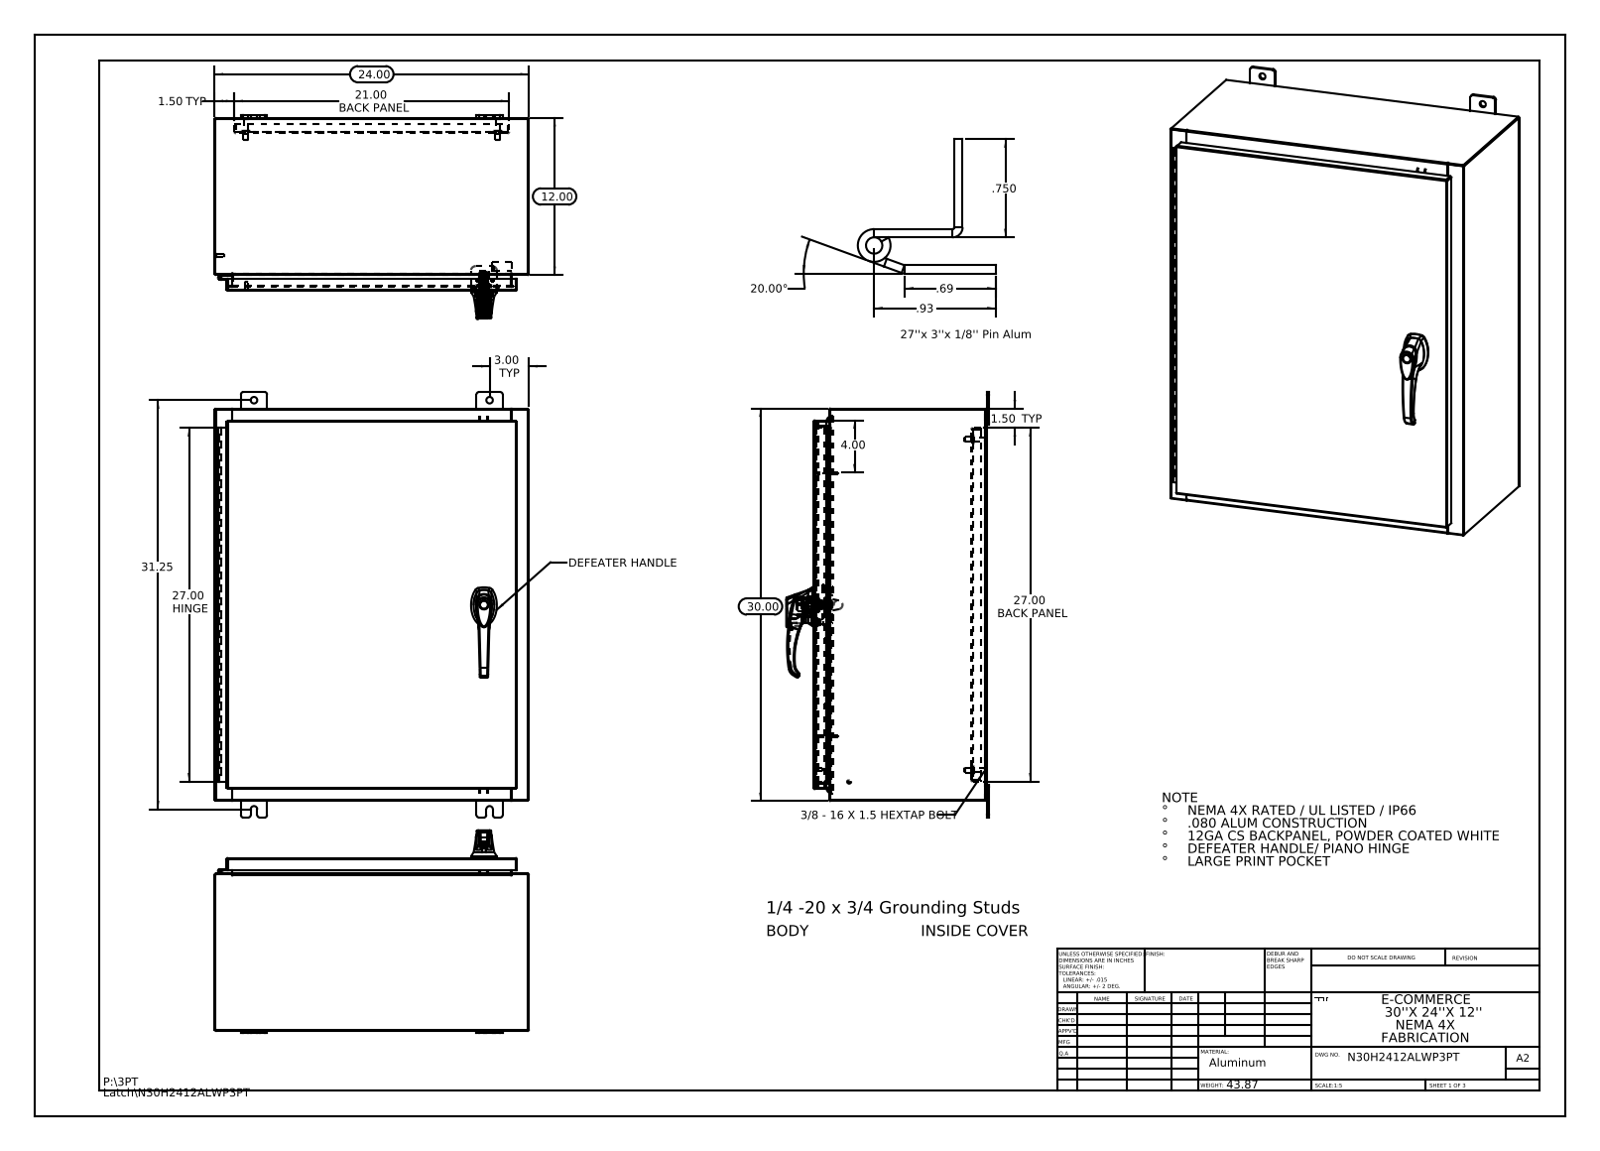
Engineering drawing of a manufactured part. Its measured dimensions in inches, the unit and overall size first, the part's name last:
Units: inches
Overall size (bounding box): 32.5 × 24 × 15.495
Round holes (diameter × count): ⌀0.5 ×8, ⌀0.25 ×4, ⌀0.138 ×3, ⌀0.161 ×3, ⌀0.079 ×2, ⌀0.203 ×2, ⌀0.313 ×2, ⌀0.437 ×2, ⌀0.125 ×1, ⌀0.125 ×1, ⌀0.197 ×1, ⌀0.276 ×1
Round bosses / shafts (diameter × count): ⌀0.625 ×4, ⌀0.375 ×4, ⌀0.33 ×4, ⌀0.157 ×4, ⌀0.14 ×4, ⌀0.315 ×3, ⌀0.236 ×3, ⌀1.181 ×1
Partial cylindrical surfaces — rounded edges, fillets, slot ends (radius × count): R0.118 ×37, R0.006 ×33, R0.013 ×24, R0.19 ×24, R0.088 ×18, R0.039 ×15, R0.028 ×12, R0.008 ×6
Main face-to-face distances: 0.075, 13.126, 23.925, 0.104, 13.051, 13.201, 1, 29.925, 1.075, 12.051
Hole centre spacings: 8.369, 0.295, 0.625, 0.841, 1.25, 1.313, 1.561, 1.858
Volume: 304.2 in³ · Surface area: 7 576 in²
Bodies: 37 solids, 2662 faces (971 planar, 993 cylindrical, 698 other)
Part name (STEP PRODUCT): N30H2412ALWP3PT Bottom; N30H2412ALWP3PT Defeater Handle - 3 - 2500-51 ZN; 022151; Quarter-20 CD Stud (+8 more)
STEP written by: SolidWorks 2013 (CONFIG_CONTROL_DESIGN)
